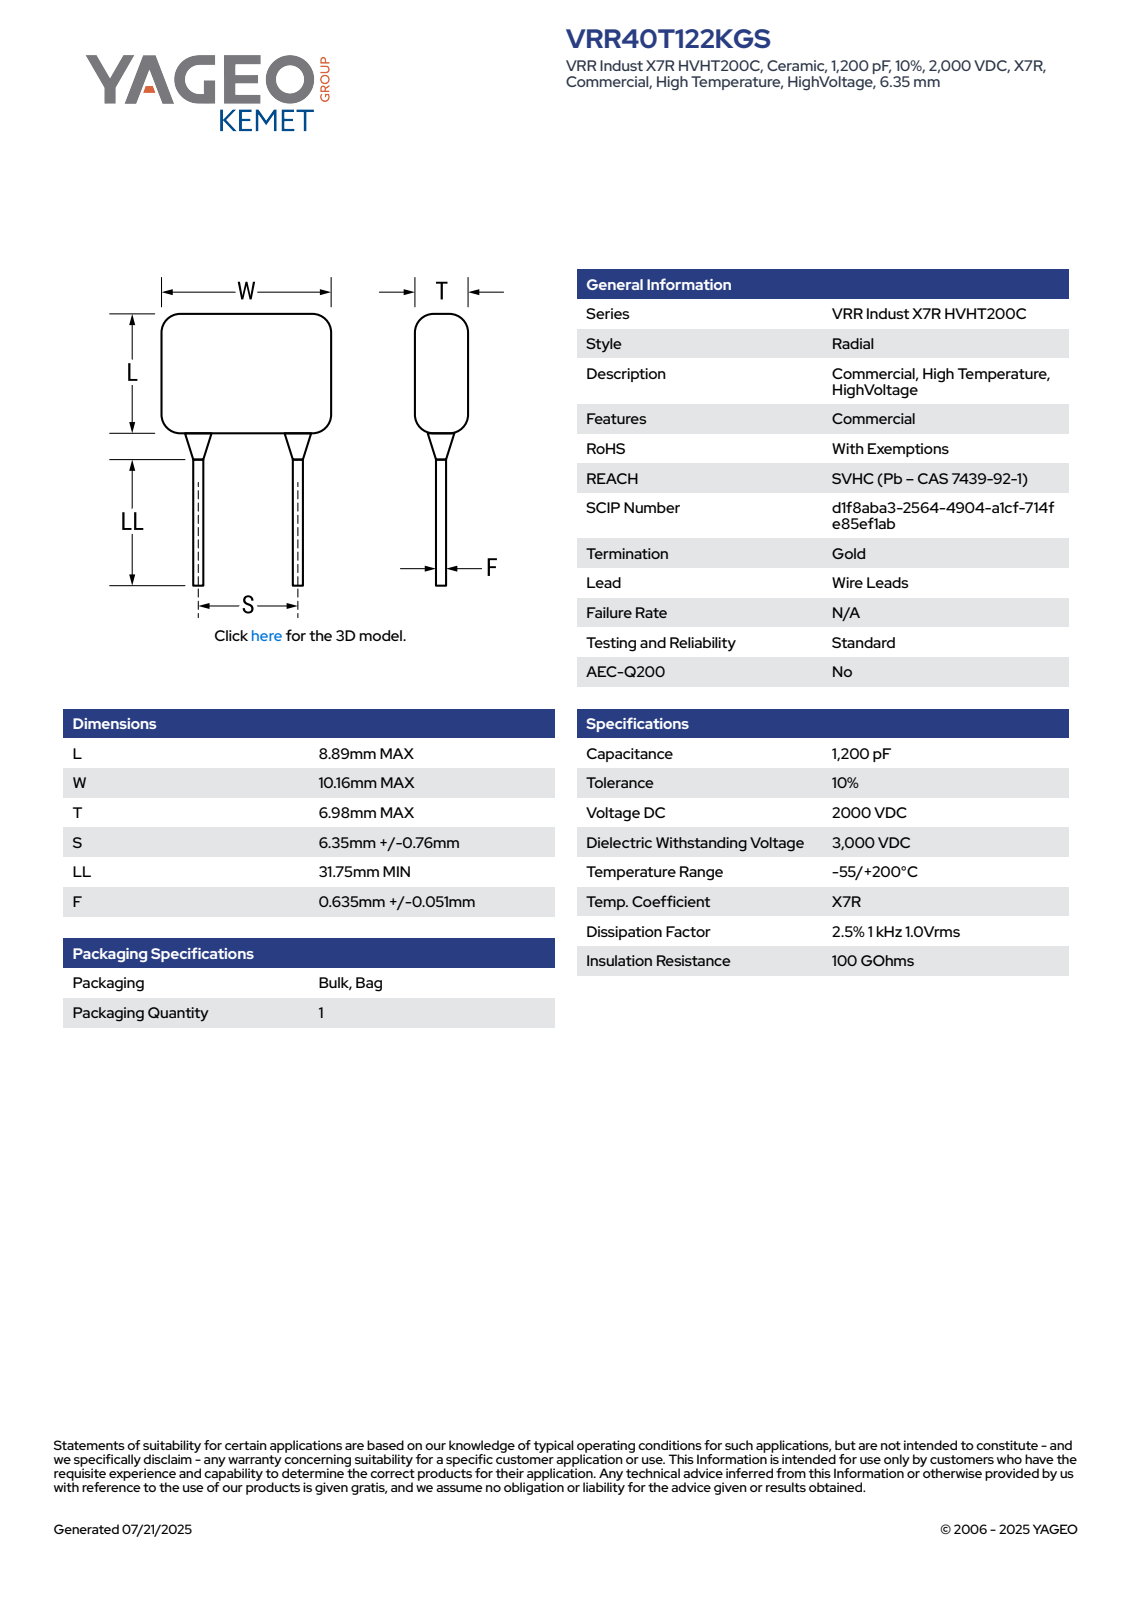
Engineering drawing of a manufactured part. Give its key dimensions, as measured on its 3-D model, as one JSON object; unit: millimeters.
{"part_name": "CCR_RMST_40_L8.89H10.16T6.98S7.11LL31.75F0.686", "step_written_by": "SolidWorks 2014 (AUTOMOTIVE_DESIGN)", "units": "millimeters", "bodies": {"solids": 4, "faces": 69, "planar": 65, "cylindrical": 4, "other": 0}, "overall_size": [41.91, 8.89, 6.99], "volume_mm3": 654, "surface_area_mm2": 595, "round_bosses_or_shafts": [[0.69, 2]], "face_to_face_distances": [6.98, 8.89, 10.16, 6.99, 31.75, 41.91, 37.48, 5.73, 4.43, 36.07]}
